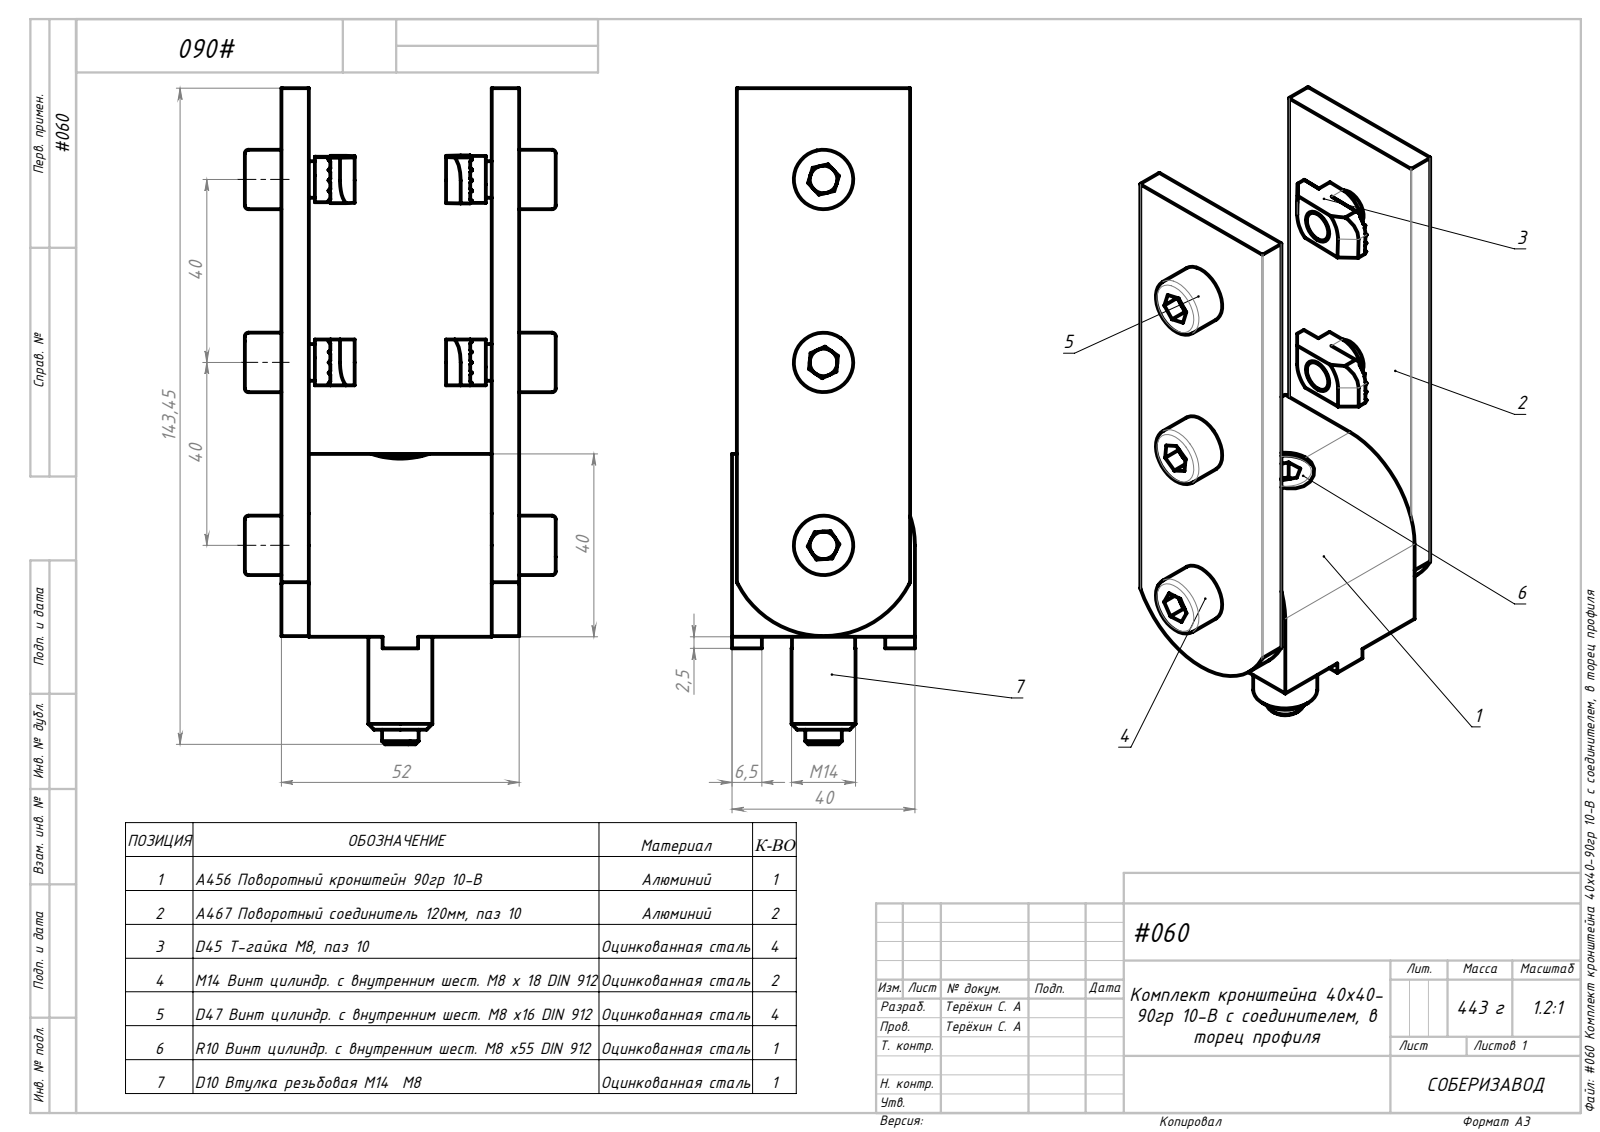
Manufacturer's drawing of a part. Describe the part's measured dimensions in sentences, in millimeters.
The part is named "D47 Винт цилиндр. с внутренним шест. М8 х16 DIN 912; #060 Комплект кронштейна 40х40-90гр 10-B с соединителем, в торец профиля; M14 Винт цилиндр. с внутренним шест. М8 х 18 DIN 912; D10 Втулка резьбовая М14 М8_00 (+4 more)". Its 3-D file was written by "SolidWorks 2021 (AUTOMOTIVE_DESIGN)". It is 15 solids with 476 faces: 291 planar, 87 cylindrical and 98 other. Overall it measures 143.45 by 68 by 40 millimeters. Its volume is 127 490 cubic millimeters and its surface area 45 635 square millimeters. Round holes: 3 of diameter 8.5, 2 of diameter 6.7, 1 of diameter 7, 1 of diameter 7.2, 1 of diameter 8.25, 1 of diameter 12.7. Round bosses or shafts: 4 of diameter 13, 4 of diameter 8, 1 of diameter 14. Partial cylindrical surfaces (rounded edges, fillets, slot ends): 8 of radius 0.2, 8 of radius 6, 4 of radius 5.67, 1 of radius 20, 1 of radius 21.12. The main face-to-face distances are 6, 46, 40, 52, 1.05, 38.95, 37.9, 10, 8, 16. The hole center spacings are 40, 80.
